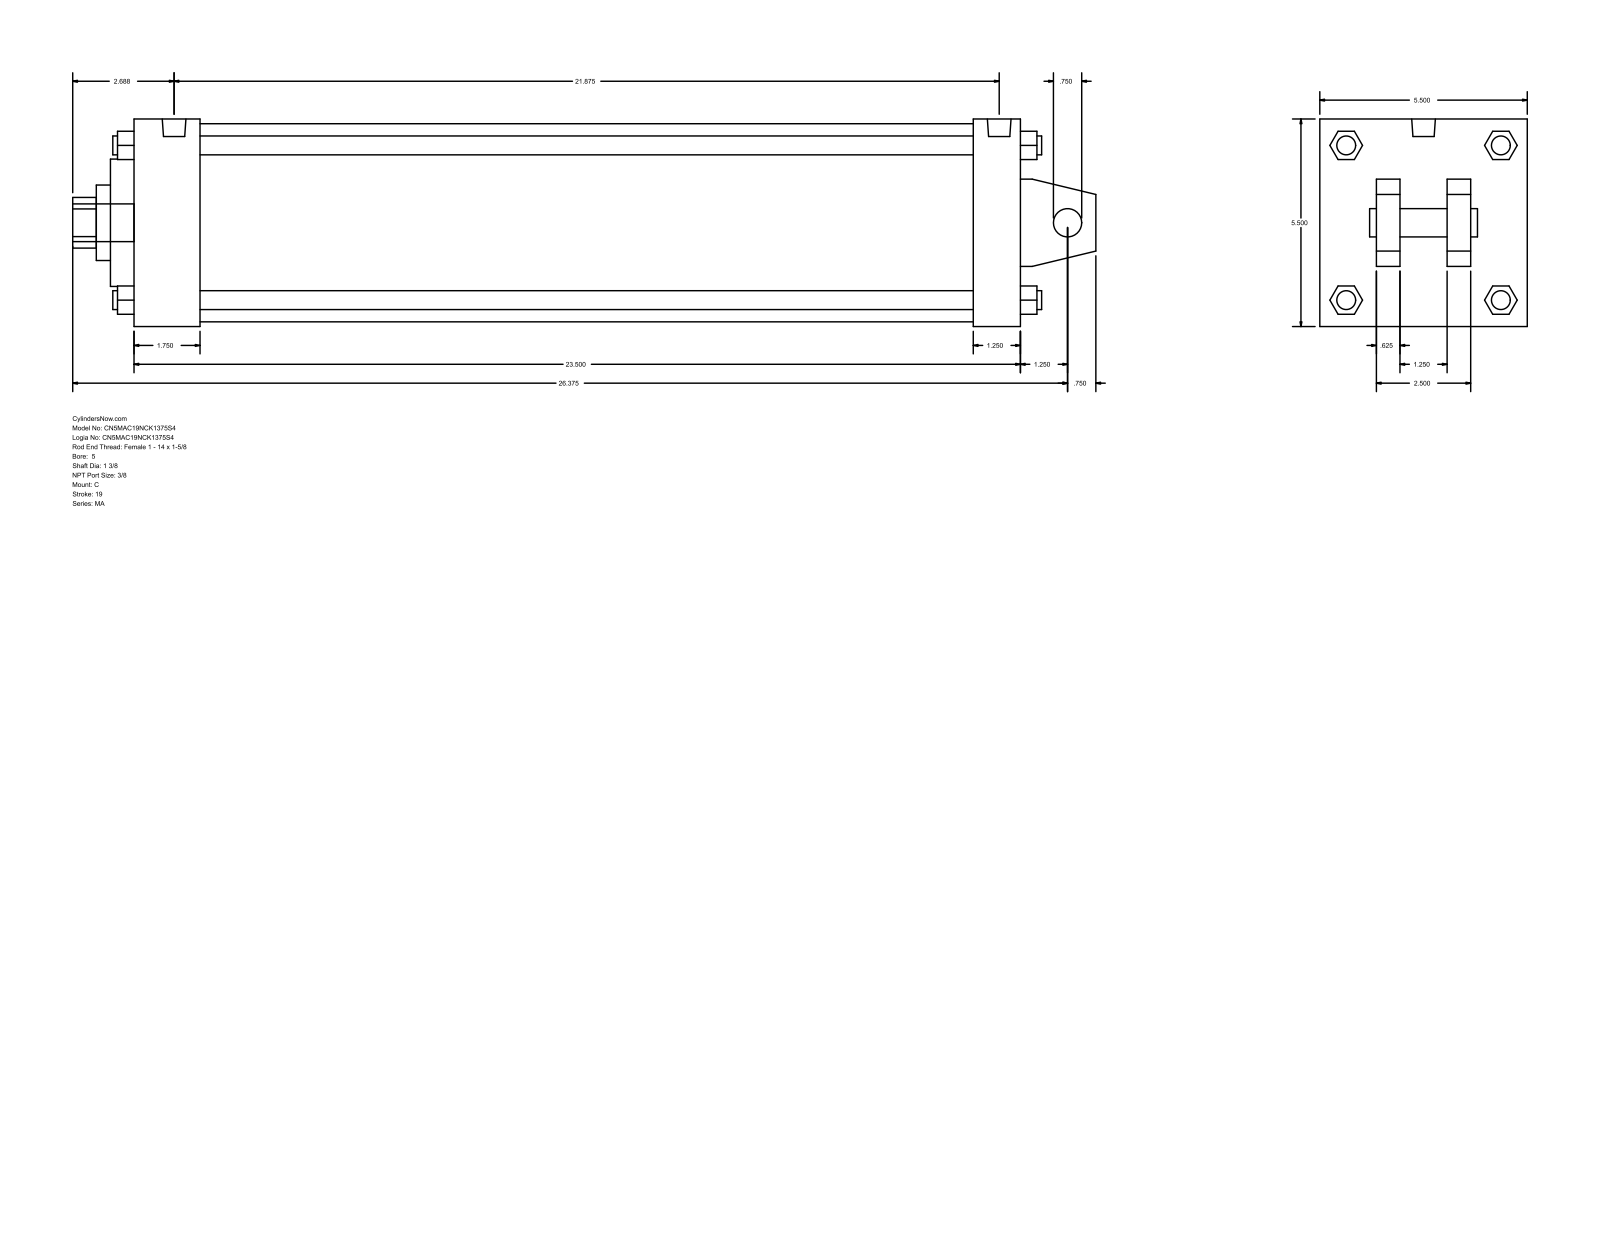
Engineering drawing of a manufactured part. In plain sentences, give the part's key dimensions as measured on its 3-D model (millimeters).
The part is named "MA_C__0500_1.375". Its 3-D file was written by "GSSL Pune (CONFIG_CONTROL_DESIGN)". It is 0 solids with 141 faces: 109 planar, 32 cylindrical and 0 other. Overall it measures 688.98 by 139.7 by 139.7 millimeters. Round holes: 1 of diameter 19.05, 1 of diameter 34.92, 1 of diameter 50.8, 1 of diameter 85.72, 1 of diameter 133.35. Round bosses or shafts: 4 of diameter 12.7, 4 of diameter 11.11, 2 of diameter 15.93, 1 of diameter 25.4. Partial cylindrical surfaces (rounded edges, fillets, slot ends): 1 of radius 17.06. The main face-to-face distances are 139.7, 596.9, 15.87, 565.15, 31.75, 44.45, 520.7, 552.45, 38.1, 101.6.
